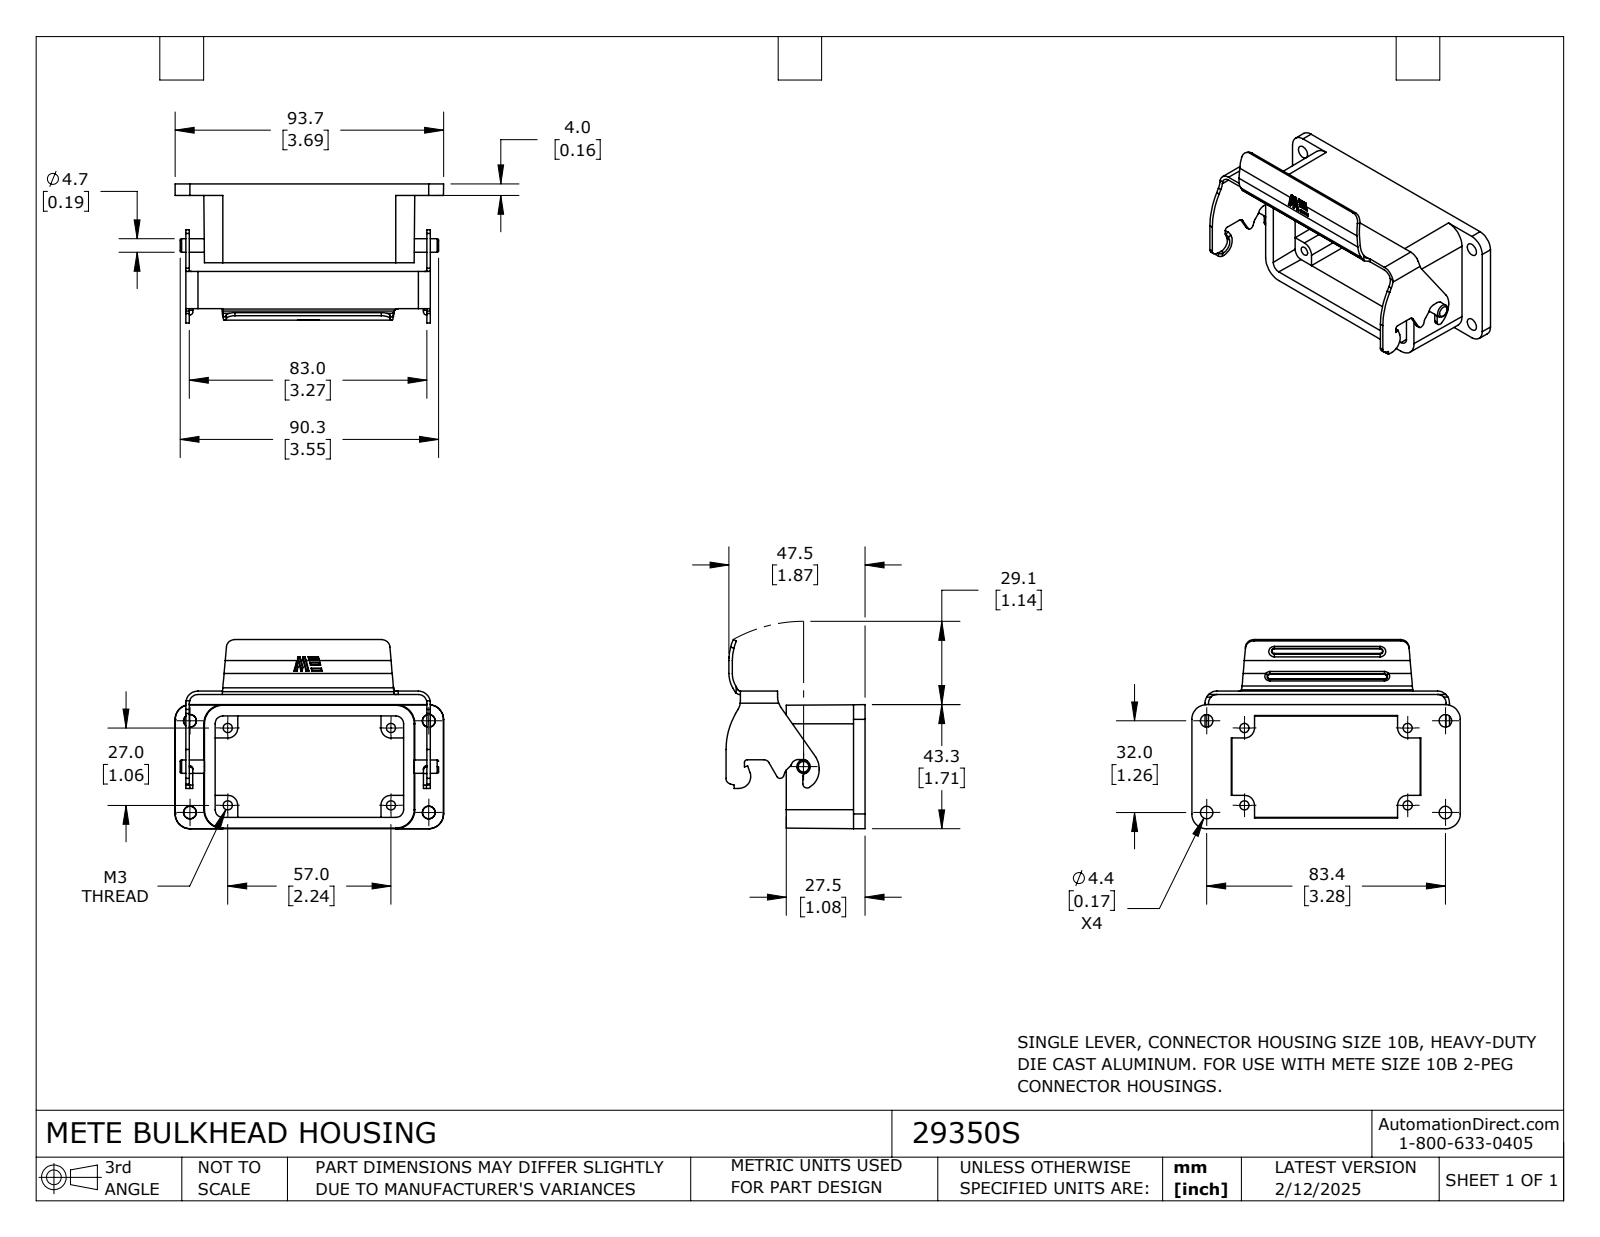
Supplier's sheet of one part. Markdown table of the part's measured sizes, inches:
| quantity | value |
| --- | --- |
| part name | 29350S |
| STEP written by | SolidWorks 2024 (CONFIG_CONTROL_DESIGN) |
| units | inches |
| bodies | 1 solid, 244 faces (97 planar, 105 cylindrical, 42 other) |
| overall size | 3.691 × 2.601 × 1.911 |
| volume | 1.979 in³ |
| surface area | 37.53 in² |
| round holes (diameter × count) | 0.126 × 4 |
| round bosses / shafts (diameter × count) | 0.185 × 1 |
| partial cylindrical surfaces (radius × count) | 0.008 × 20, 0.039 × 10, 0.118 × 5, 0.138 × 4, 0.031 × 3, 0.079 × 3, 0.098 × 3, 0.165 × 3 |
| main face-to-face distances | 0.047, 3.315, 0.157, 1.409, 1.697, 1.744, 0.287, 0.335, 1.083, 0.925 |
| hole center spacings | 1.063, 2.244, 2.483 |
